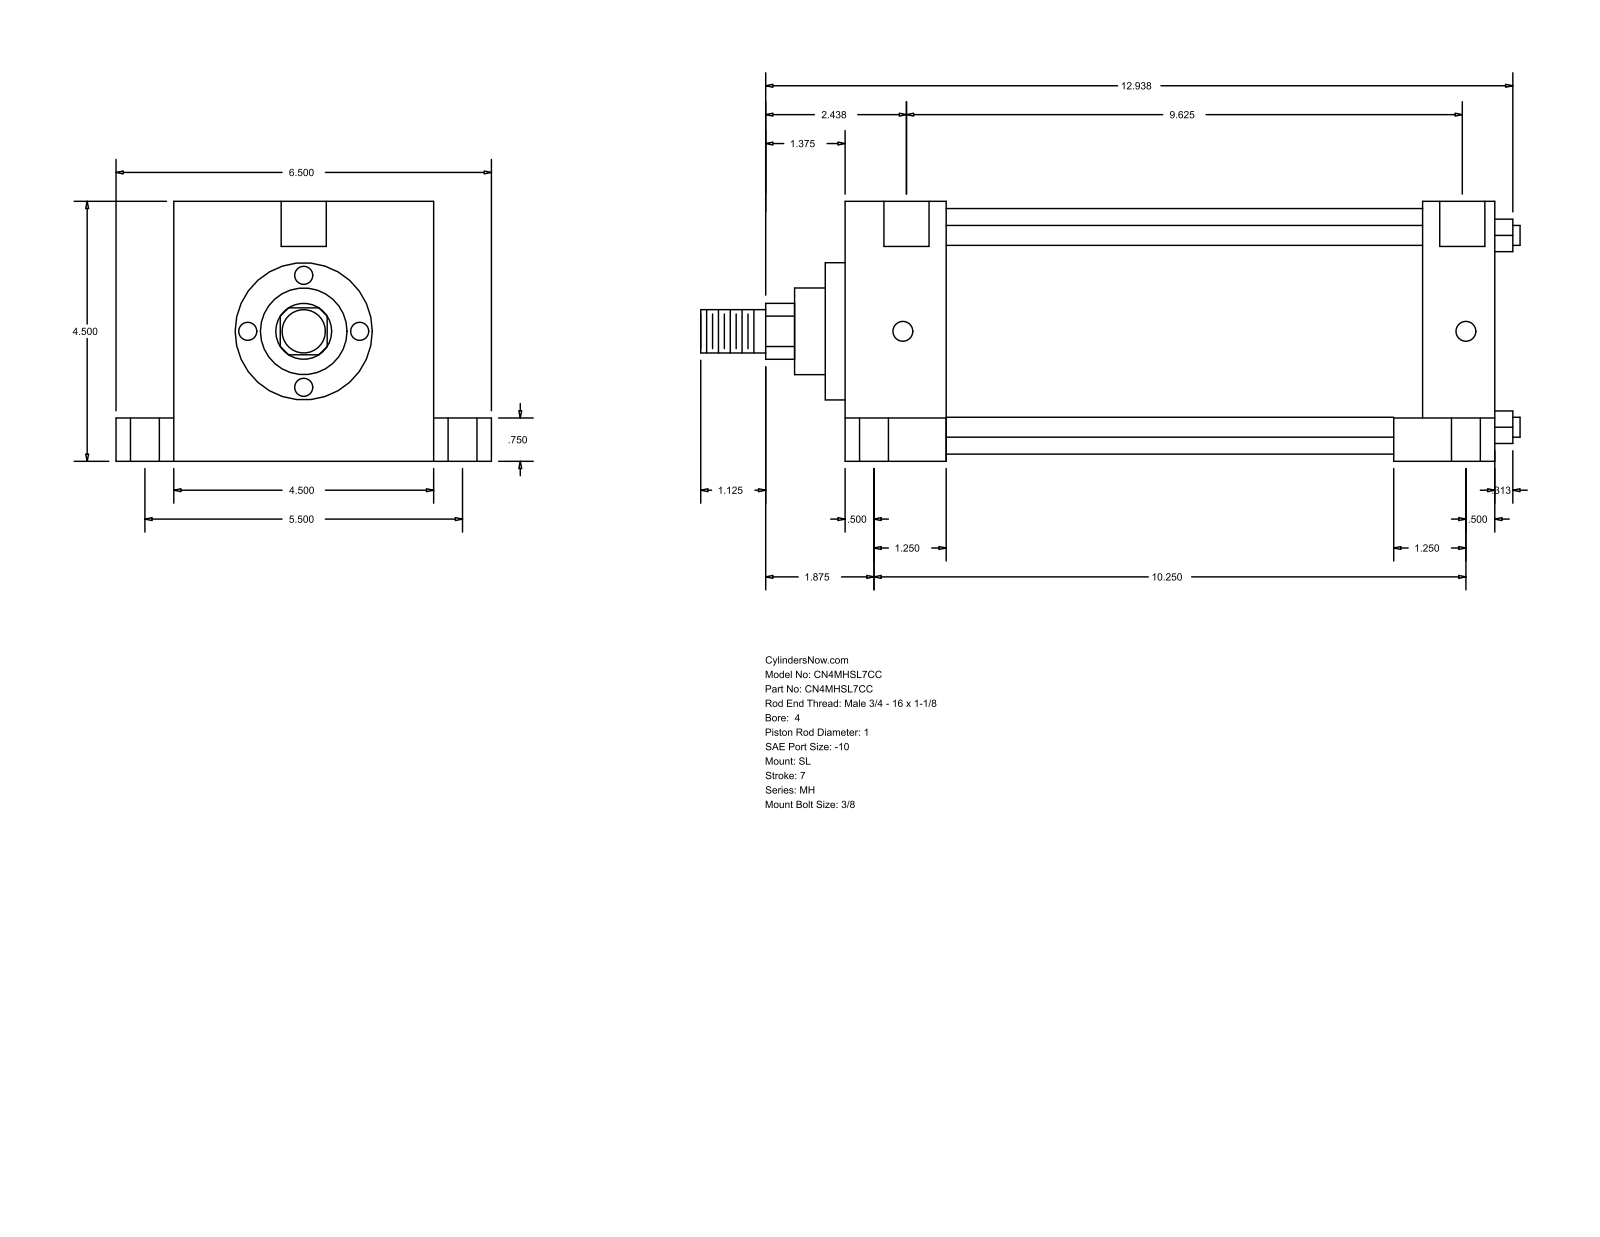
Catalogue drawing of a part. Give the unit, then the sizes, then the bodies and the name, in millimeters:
Units: millimetres
Overall size (bounding box): 360.36 × 165.1 × 114.3
Round holes (diameter × count): ⌀8.73 ×4, ⌀12.7 ×4, ⌀19.05 ×4, ⌀19.84 ×2
Round bosses / shafts (diameter × count): ⌀8.76 ×4, ⌀107.95 ×1, ⌀60.33 ×1, ⌀38.1 ×1, ⌀25.4 ×1, ⌀19.05 ×1
Partial cylindrical surfaces — rounded edges, fillets, slot ends (radius × count): R12.29 ×1
Main face-to-face distances: 114.3, 285.76, 44.46, 241.3, 254.01, 209.55, 31.75, 25.4, 139.7, 19.05
Hole centre spacings: 69.85, 69.87, 71, 71.3, 139.7, 247.65, 255.79, 257.31
Bodies: 0 solids, 110 faces (77 planar, 33 cylindrical, 0 other)
Part name (STEP PRODUCT): MH_SL__0400_1
STEP written by: GSSL Pune (CONFIG_CONTROL_DESIGN)
